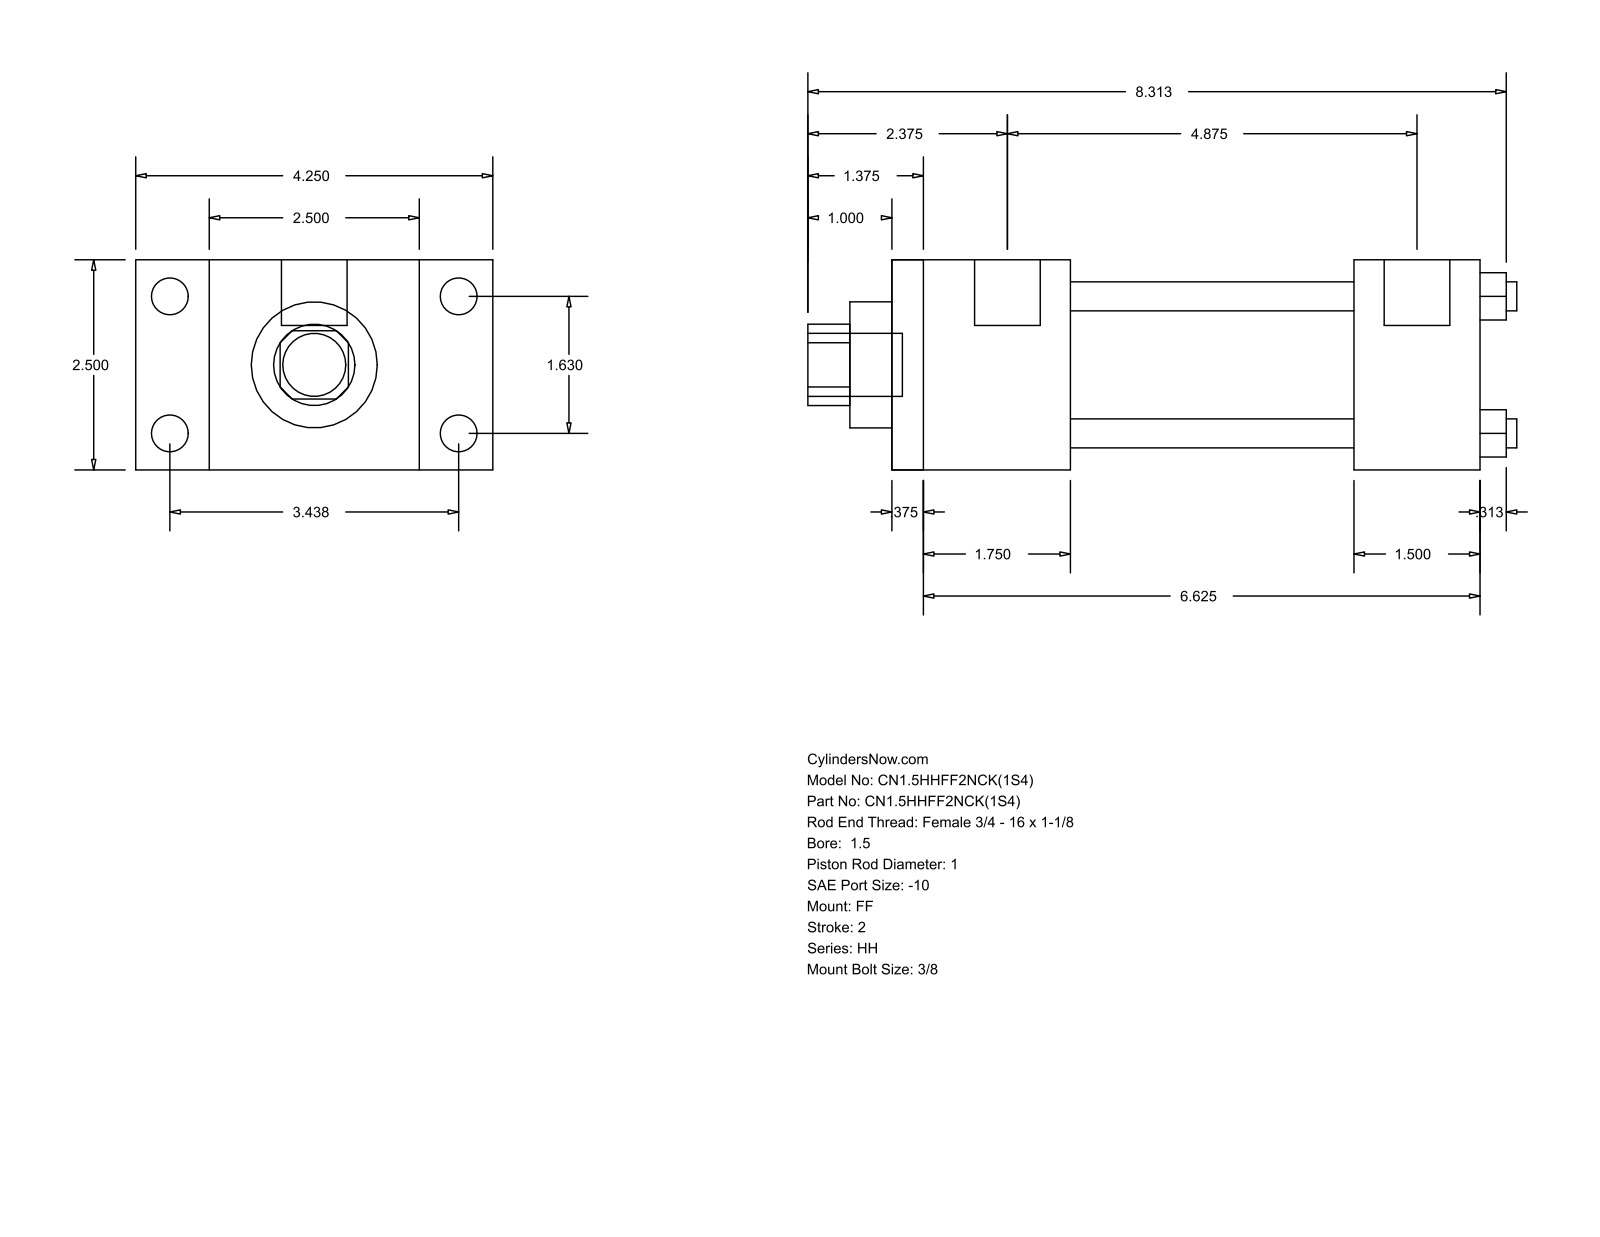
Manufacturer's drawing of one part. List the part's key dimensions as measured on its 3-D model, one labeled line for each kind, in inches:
Part name (STEP PRODUCT): HH_FF__0150_1
STEP written by: GSSL Pune (CONFIG_CONTROL_DESIGN)
Units: inches
Bodies: 0 solids, 92 faces (64 planar, 28 cylindrical, 0 other)
Overall size (bounding box): 8.437 × 4.25 × 2.5
Round holes (diameter × count): ⌀0.345 ×4, ⌀1 ×1, ⌀1.5 ×1, ⌀1.75 ×1
Round bosses / shafts (diameter × count): ⌀0.438 ×4, ⌀0.219 ×4, ⌀0.781 ×2, ⌀0.75 ×1
Partial cylindrical surfaces — rounded edges, fillets, slot ends (radius × count): R0.484 ×1
Main face-to-face distances: 2.5, 7, 0.375, 6.625, 2.125, 1.75, 4.875, 5.5, 5.125, 3.375
Hole centre spacings: 1.152, 1.63, 2.305
